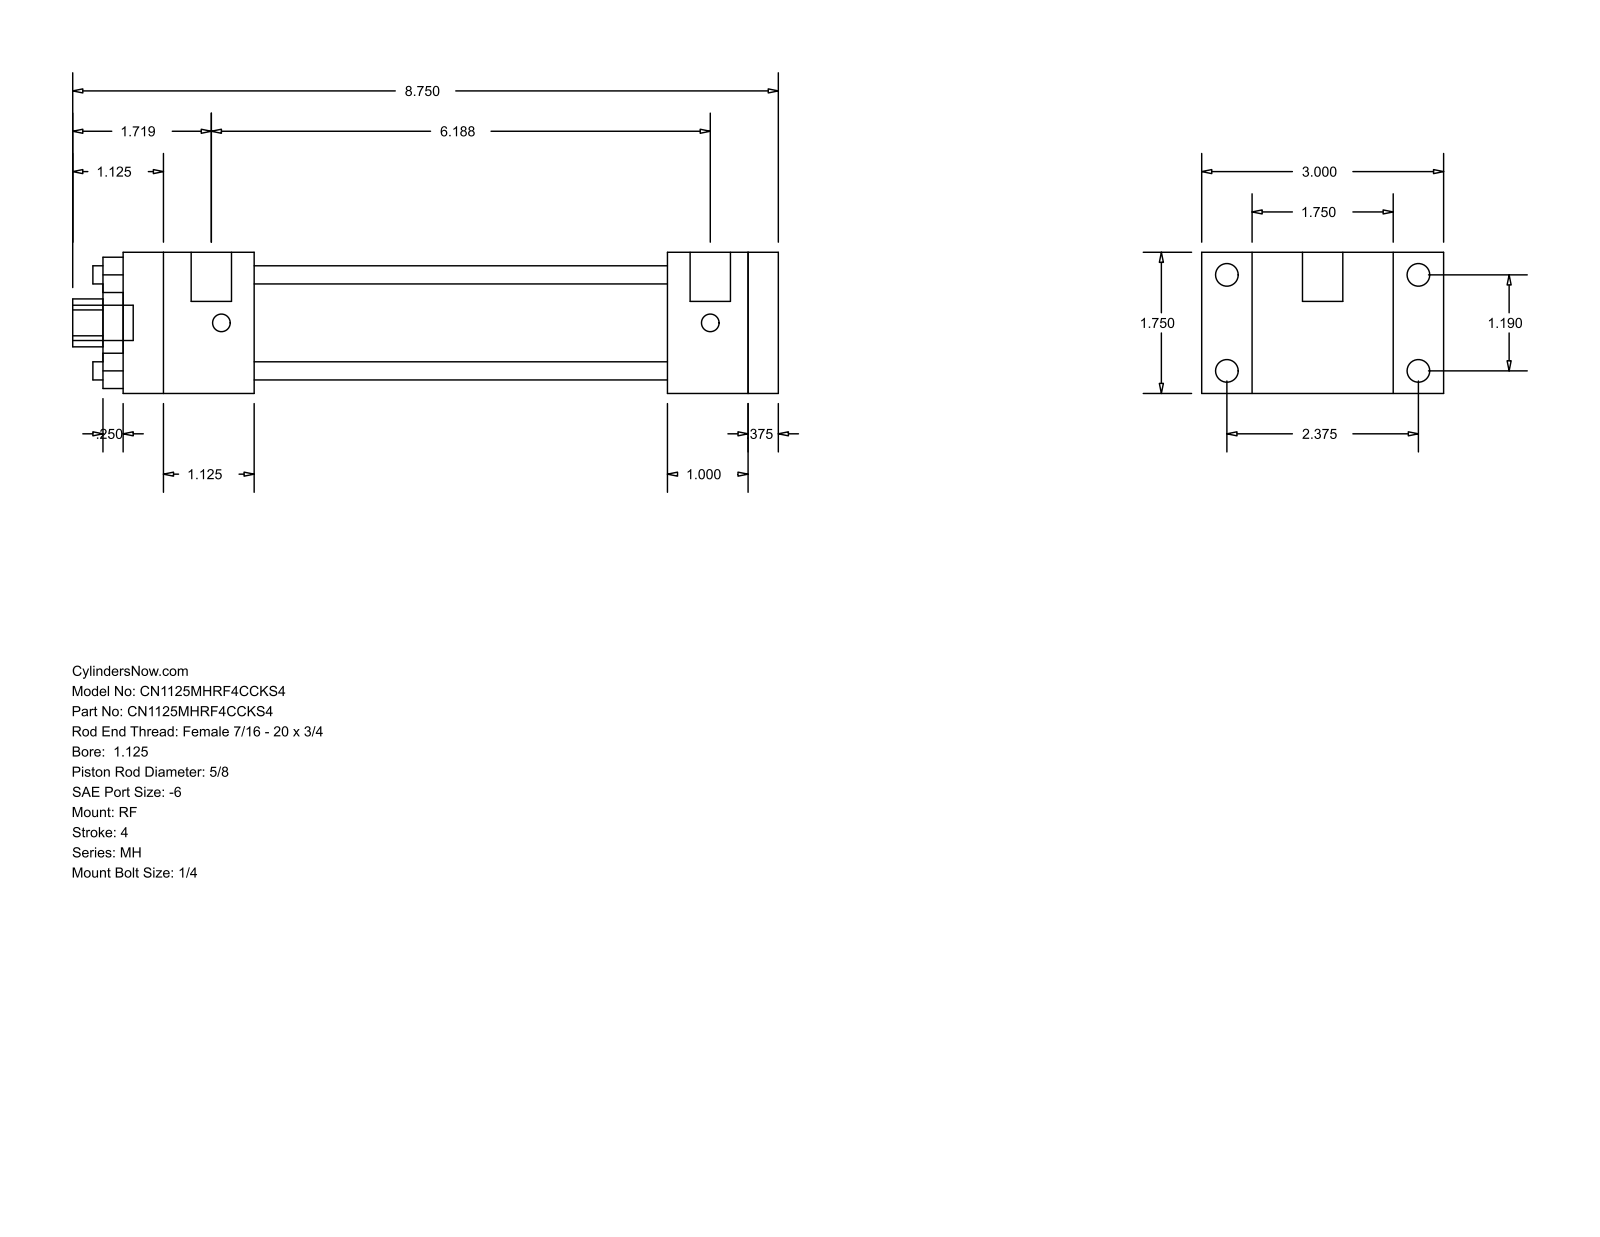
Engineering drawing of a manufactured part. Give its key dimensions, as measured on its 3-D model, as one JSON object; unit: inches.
{"part_name": "MH_RF__0112_0.625", "step_written_by": "GSSL Pune (CONFIG_CONTROL_DESIGN)", "units": "inches", "bodies": {"solids": 0, "faces": 92, "planar": 64, "cylindrical": 28, "other": 0}, "overall_size": [8.75, 3, 1.75], "round_holes": [[0.225, 4], [0.625, 1], [1.125, 1], [1.375, 1]], "round_bosses_or_shafts": [[0.281, 4], [0.219, 4], [0.5, 2], [0.437, 1]], "partial_cylinders_radius": [[0.297, 1]], "face_to_face_distances": [1.75, 0.375, 8.125, 0.625, 6.125, 6.5, 5.125, 1, 1.375, 1.625], "hole_center_spacings": [0.841, 1.19, 1.683]}
